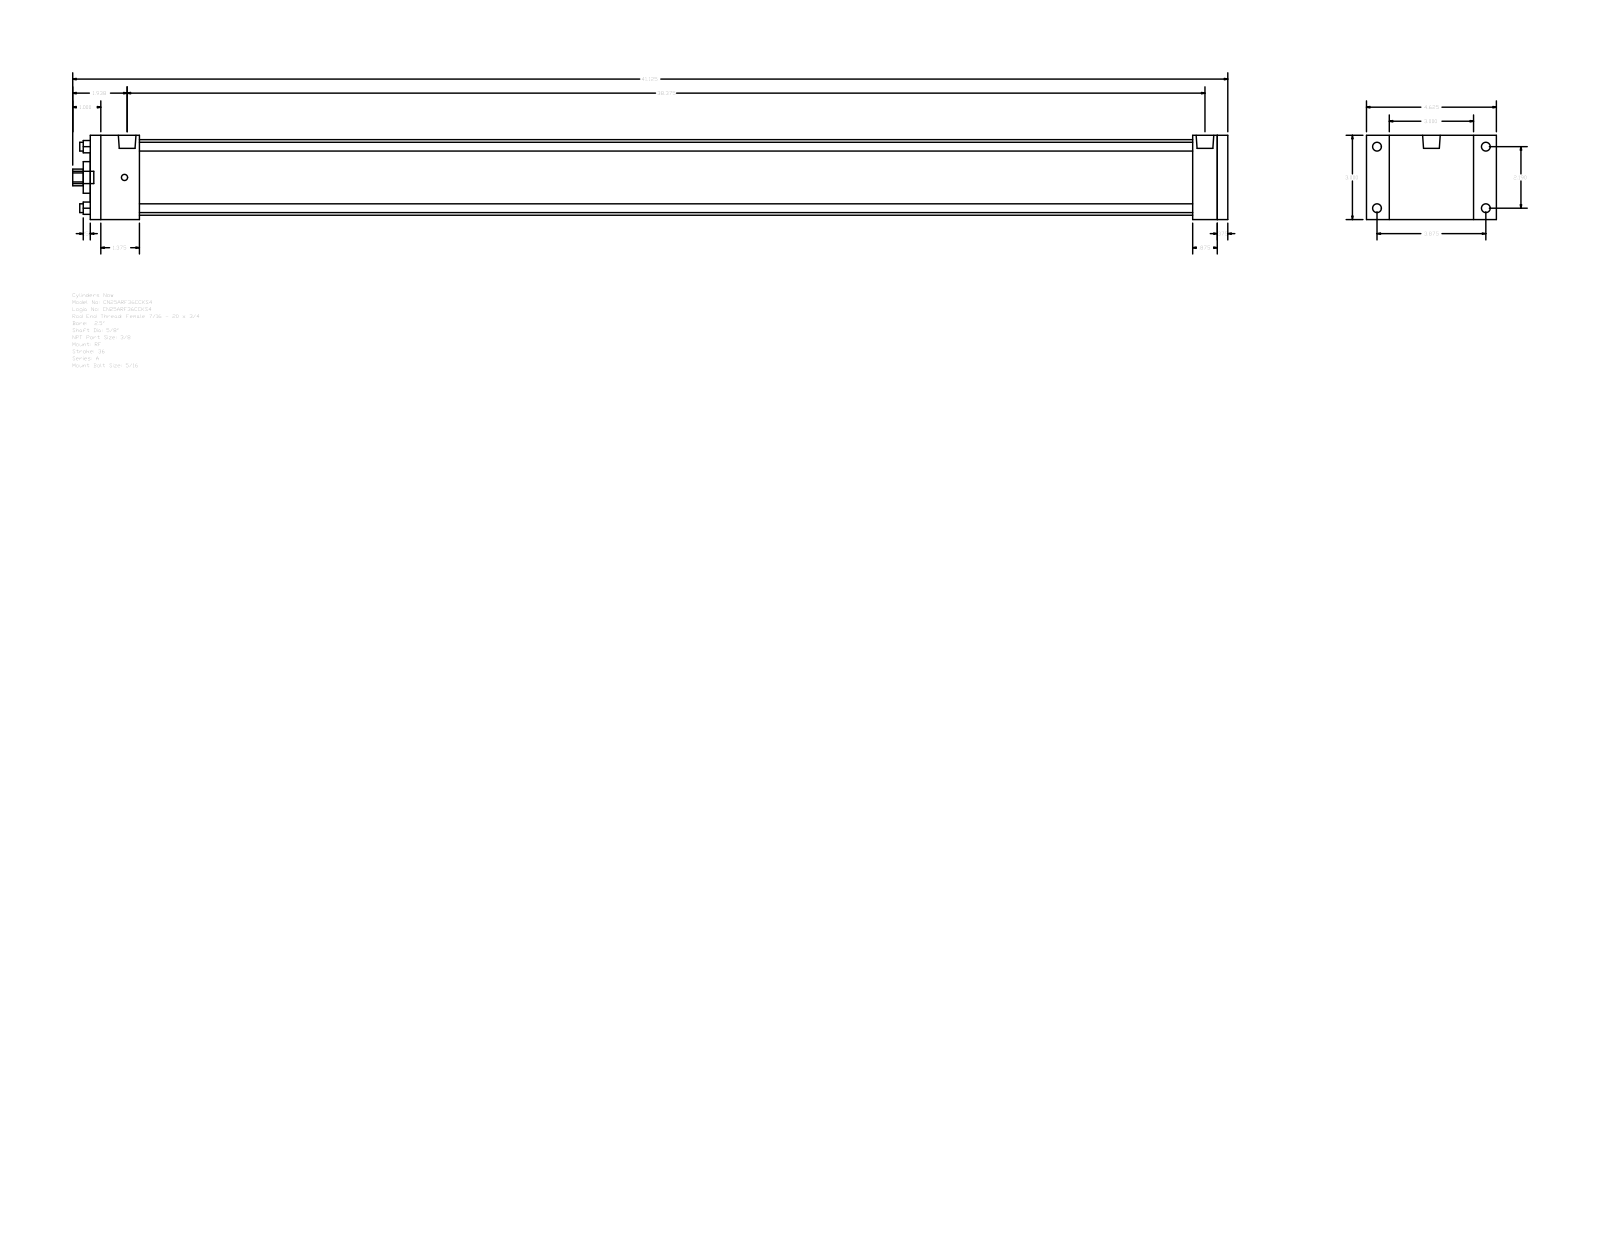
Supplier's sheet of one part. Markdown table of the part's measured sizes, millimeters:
| quantity | value |
| --- | --- |
| part name | A_RF__0250_0.625 |
| STEP written by | GSSL Pune (CONFIG_CONTROL_DESIGN) |
| units | millimeters |
| bodies | 0 solids, 92 faces (64 planar, 28 cylindrical, 0 other) |
| overall size | 1044.58 × 117.47 × 76.2 |
| round holes (diameter × count) | 7.94 × 4, 15.88 × 1, 28.57 × 1, 68.33 × 1 |
| round bosses / shafts (diameter × count) | 7.94 × 4, 5.56 × 4, 15.93 × 2, 11.11 × 1 |
| partial cylindrical surfaces (radius × count) | 7.54 × 1 |
| main face-to-face distances | 76.2, 1028.7, 9.53, 1019.17, 44.45, 31.75, 996.95, 952.5, 974.72, 984.25 |
| hole center spacings | 39.33, 55.62, 78.66 |
